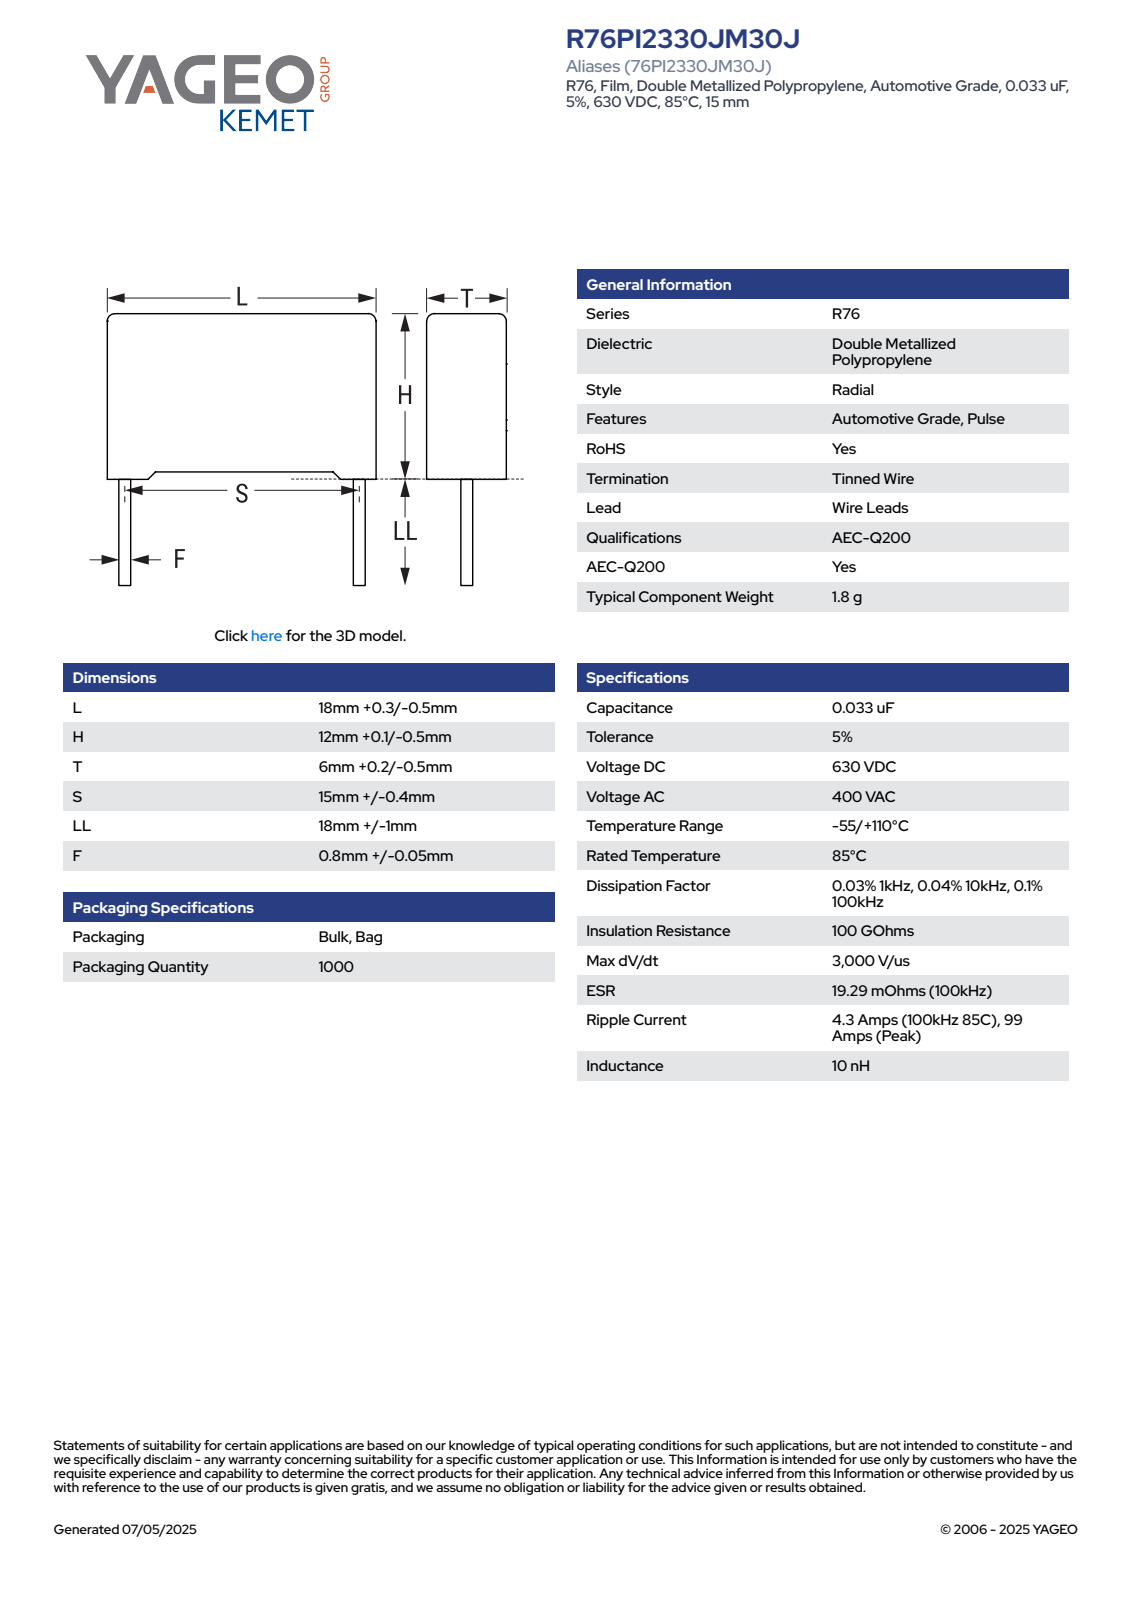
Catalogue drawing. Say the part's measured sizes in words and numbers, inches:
The part is named "CFR_RB2_18X12X6_L18.3H12.1T6.2S15LL19F0.85". Its 3-D file was written by "SolidWorks 2021 (AUTOMOTIVE_DESIGN)". It is 4 solids with 85 faces: 77 planar, 8 cylindrical and 0 other. Overall it measures 1.224 by 0.72 by 0.244 inches. Its volume is 0.081 cubic inches and its surface area 1.48 square inches. Round bosses or shafts: 2 of diameter 0.033. Partial cylindrical surfaces (rounded edges, fillets, slot ends): 4 of radius 0.02. The main face-to-face distances are 0.244, 0.447, 0.72, 0.024, 0.22, 0.03, 0.476, 0.017, 0.013, 0.46.
